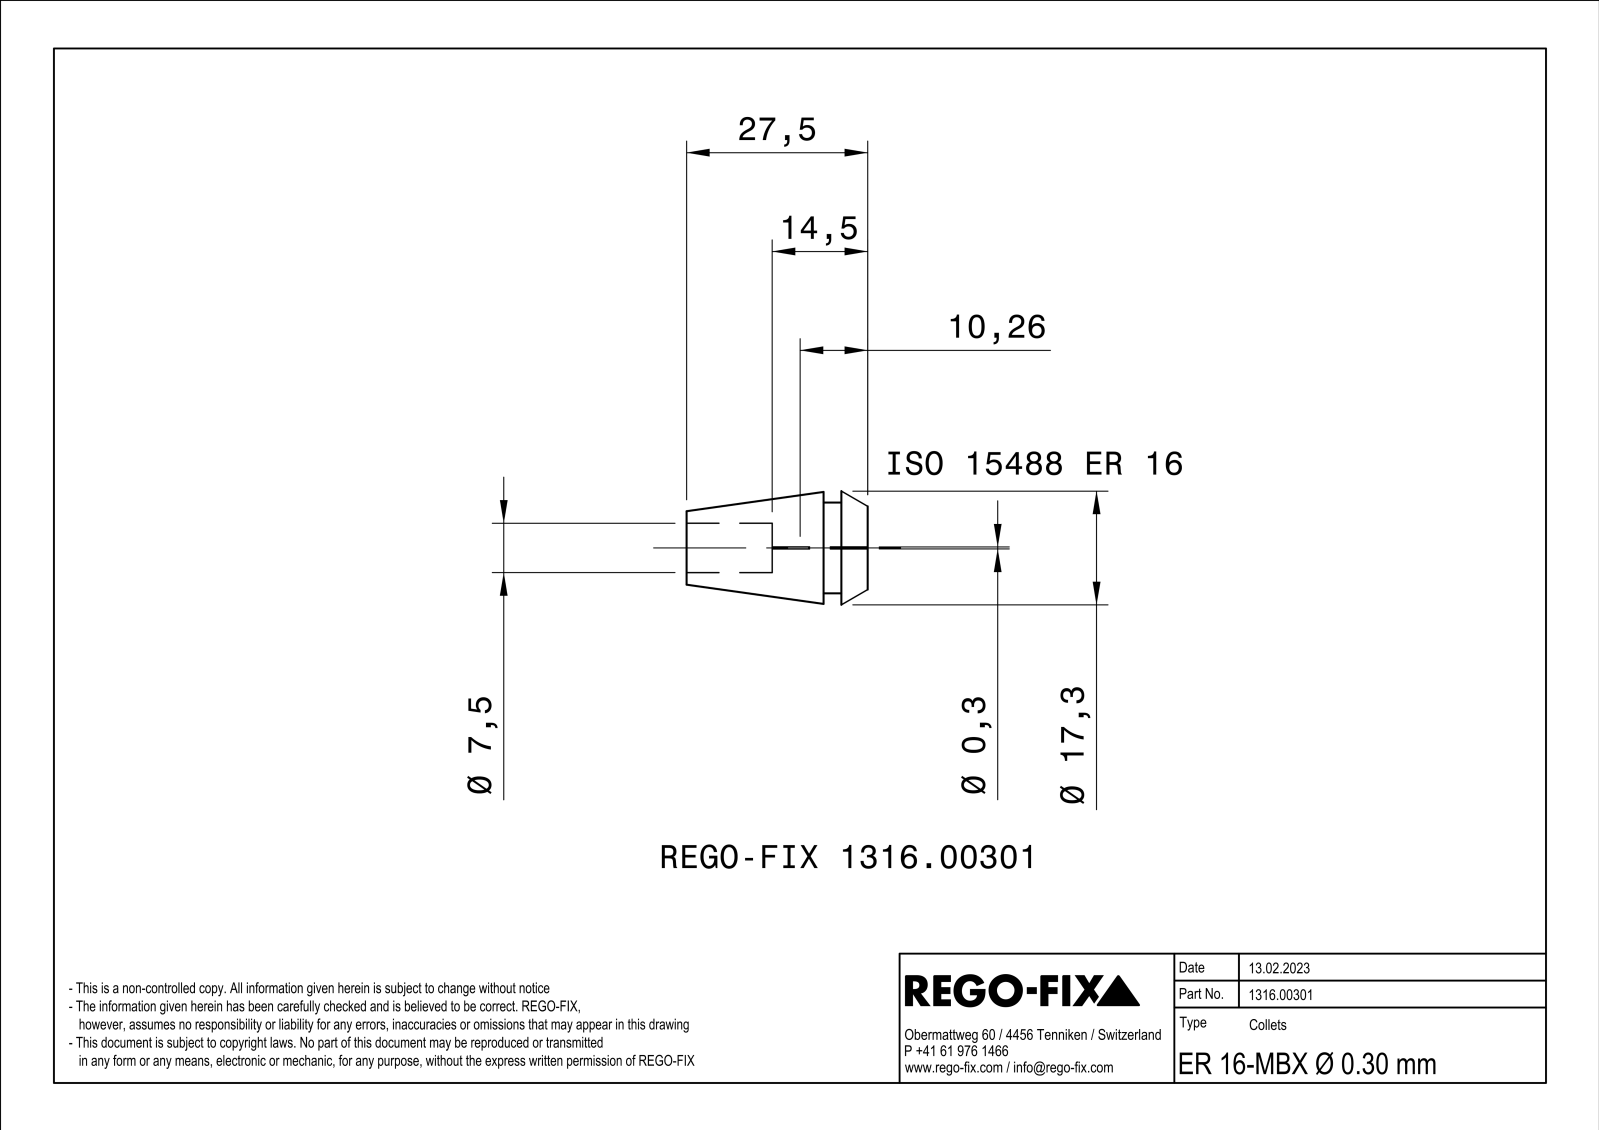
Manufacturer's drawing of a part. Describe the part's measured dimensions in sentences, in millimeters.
The part is named "NOCUT". Its 3-D file was written by "SIEMENS PLM Software Solid Edge ST10 (AUTOMOTIVE_DESIGN)". It is 1 solid with 109 faces: 36 planar, 27 cylindrical and 46 other. Overall it measures 27.5 by 16.91 by 16.9 millimeters. Its volume is 3 347 cubic millimeters and its surface area 3 341 square millimeters. Round holes: 3 of diameter 2, 1 of diameter 7.5. Round bosses or shafts: 1 of diameter 13.8. Partial cylindrical surfaces (rounded edges, fillets, slot ends): 3 of radius 25, 1 of radius 0.15. The main face-to-face distances are 0.34, 0.46, 0.8, 6.7, 4, 2.7, 27.5, 23.5, 20.8, 14.5. The hole center spacings are 2.1, 3.64.
